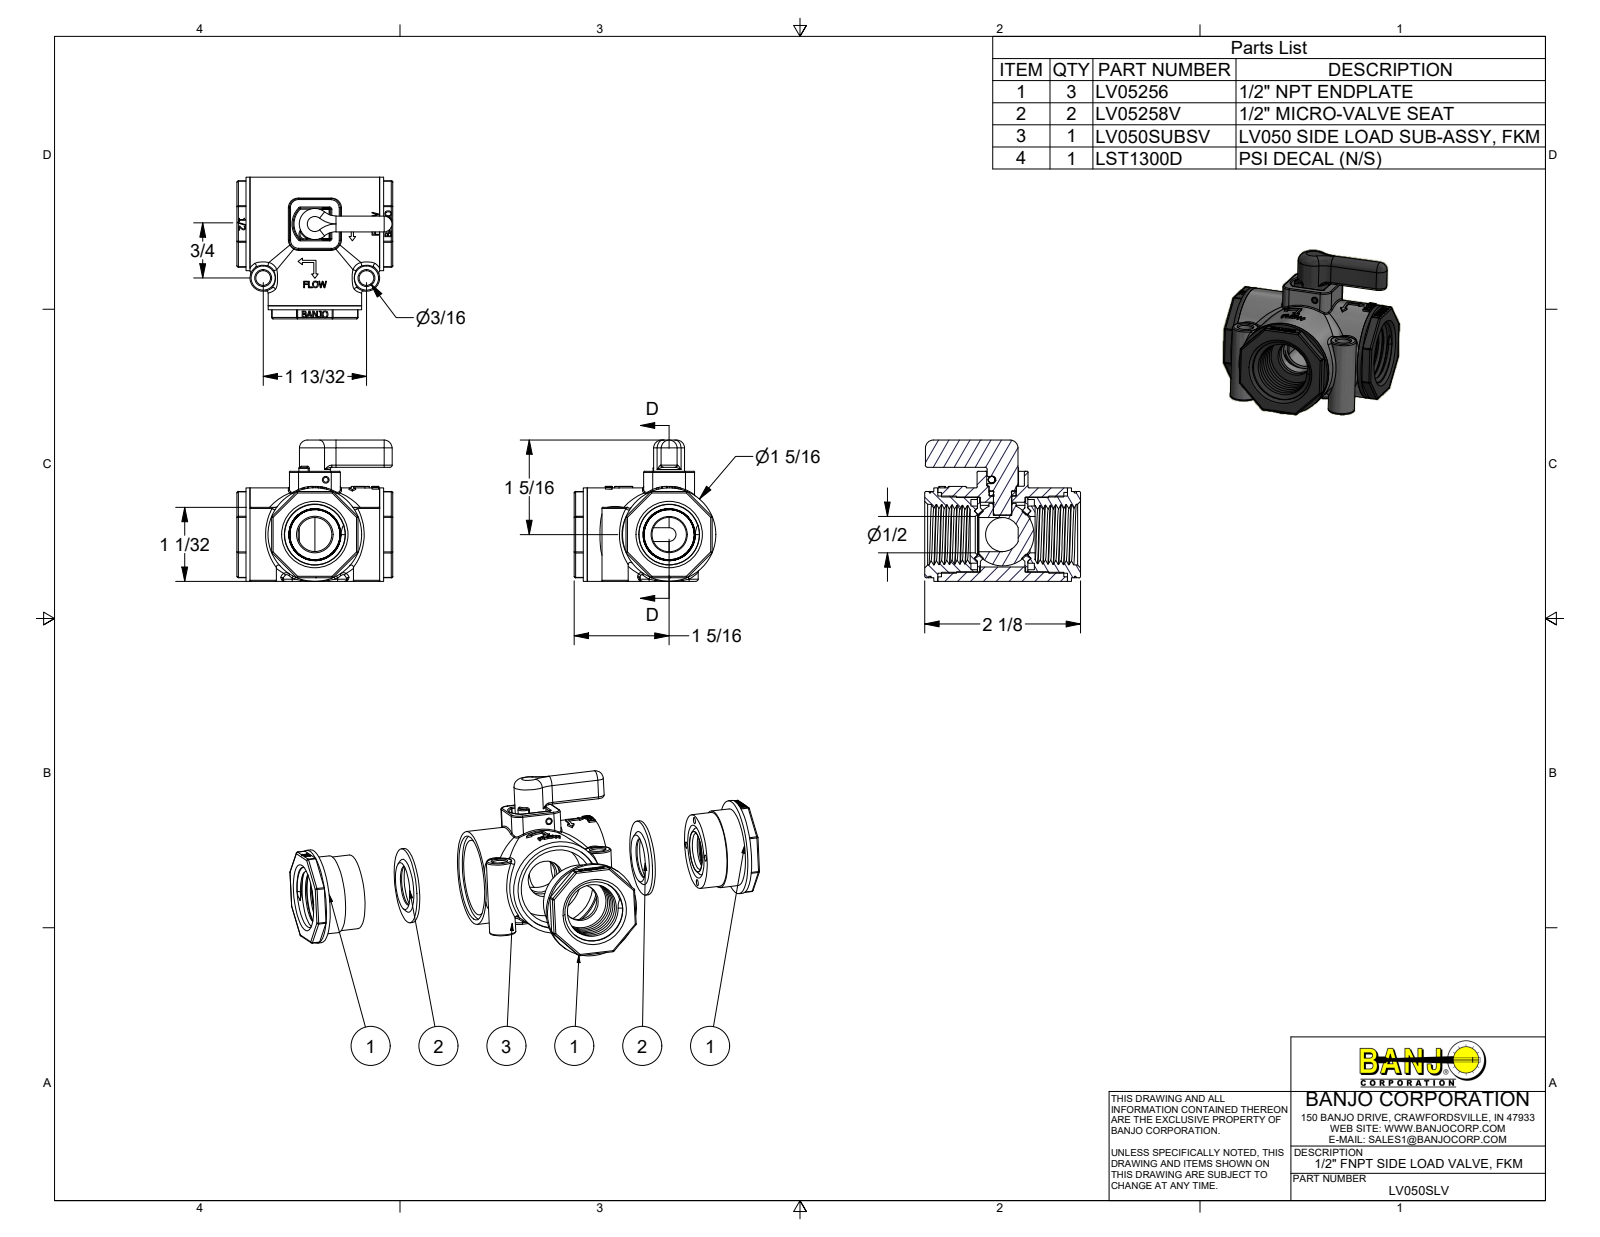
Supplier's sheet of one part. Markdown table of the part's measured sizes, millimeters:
| quantity | value |
| --- | --- |
| part name | LV05254AS; LV02153B; AQ010V; WS10002 (+5 more) |
| STEP written by | Autodesk Inventor 2014 (AUTOMOTIVE_DESIGN) |
| units | millimeters |
| bodies | 10 solids, 1058 faces (458 planar, 198 cylindrical, 402 other) |
| overall size | 54.41 × 49.47 × 49.37 |
| volume | 46 835 mm³ |
| surface area | 34 488 mm² |
| round holes (diameter × count) | 2.29 × 8, 5.11 × 2, 11.94 × 2, 12.7 × 2, 26.26 × 2, 29.46 × 2, 2.36 × 1, 6.38 × 1, 9.35 × 1, 9.55 × 1, 13.74 × 1, 22.61 × 1 |
| round bosses / shafts (diameter × count) | 32.64 × 2, 26.97 × 2, 25.91 × 2, 9.17 × 2, 26.01 × 1, 10.79 × 1, 9.52 × 1, 9.45 × 1 |
| partial cylindrical surfaces (radius × count) | 0.51 × 40, 0.38 × 18, 0.25 × 16, 3.17 × 8, 0.76 × 7, 1.27 × 2, 2.77 × 2, 6.35 × 2 |
| main face-to-face distances | 13.84, 31.42, 14.6, 18.41, 4.57, 35.99, 49.83, 0.76, 2.54, 19.43 |
| hole center spacings | 11.14, 15.75, 22.28, 11.11, 11.17, 26.11, 8.87, 19.5 |
